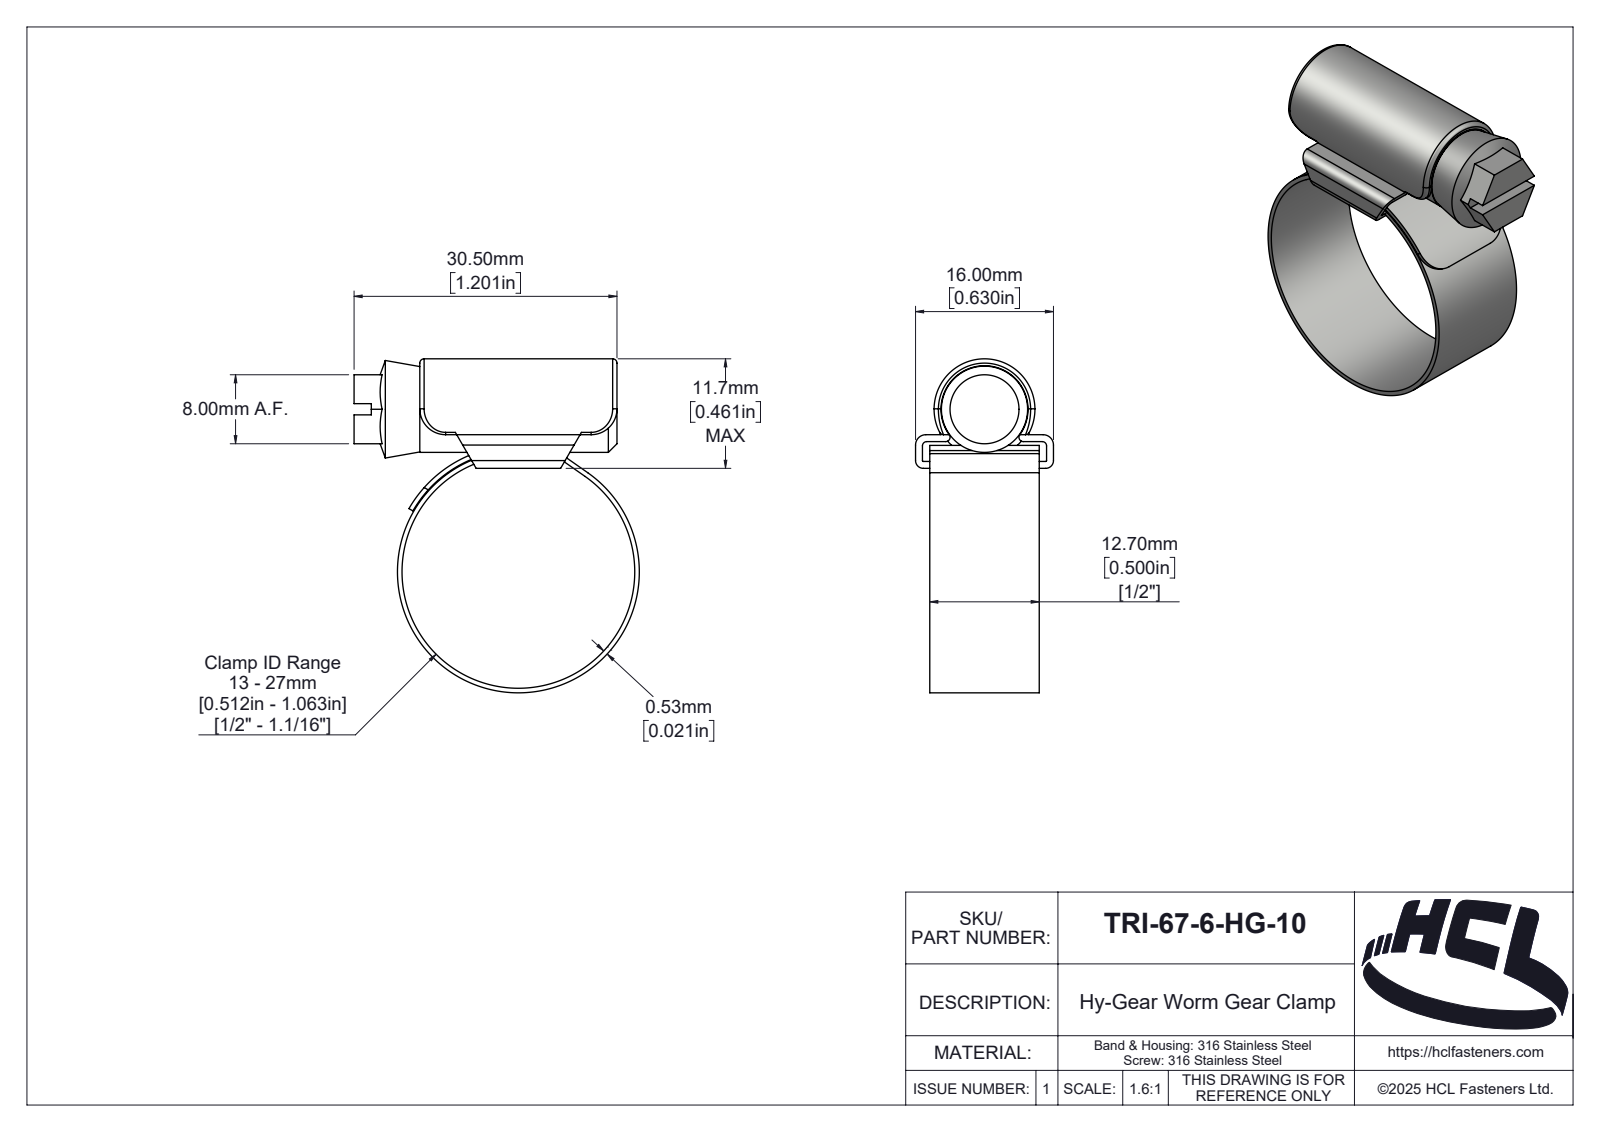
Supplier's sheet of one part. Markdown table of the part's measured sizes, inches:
| quantity | value |
| --- | --- |
| part name | TRI-57-0-HG-10 |
| STEP written by | SolidWorks 2025 (AUTOMOTIVE_DESIGN) |
| units | inches |
| bodies | 3 solids, 189 faces (39 planar, 89 cylindrical, 61 other) |
| overall size | 1.525 × 1.303 × 0.63 |
| volume | 0.224 in³ |
| surface area | 8.678 in² |
| round holes (diameter × count) | 1.063 × 1 |
| round bosses / shafts (diameter × count) | 1.105 × 1, 0.394 × 1 |
| partial cylindrical surfaces (radius × count) | 0.02 × 6, 0.118 × 4, 0.004 × 2, 0.035 × 2, 0.047 × 2, 0.018 × 1, 0.074 × 1, 0.079 × 1 |
| main face-to-face distances | 0.031, 0.122, 0.091, 0.154, 0.5, 0.021, 1.201, 0.065, 0.565, 0.598 |
